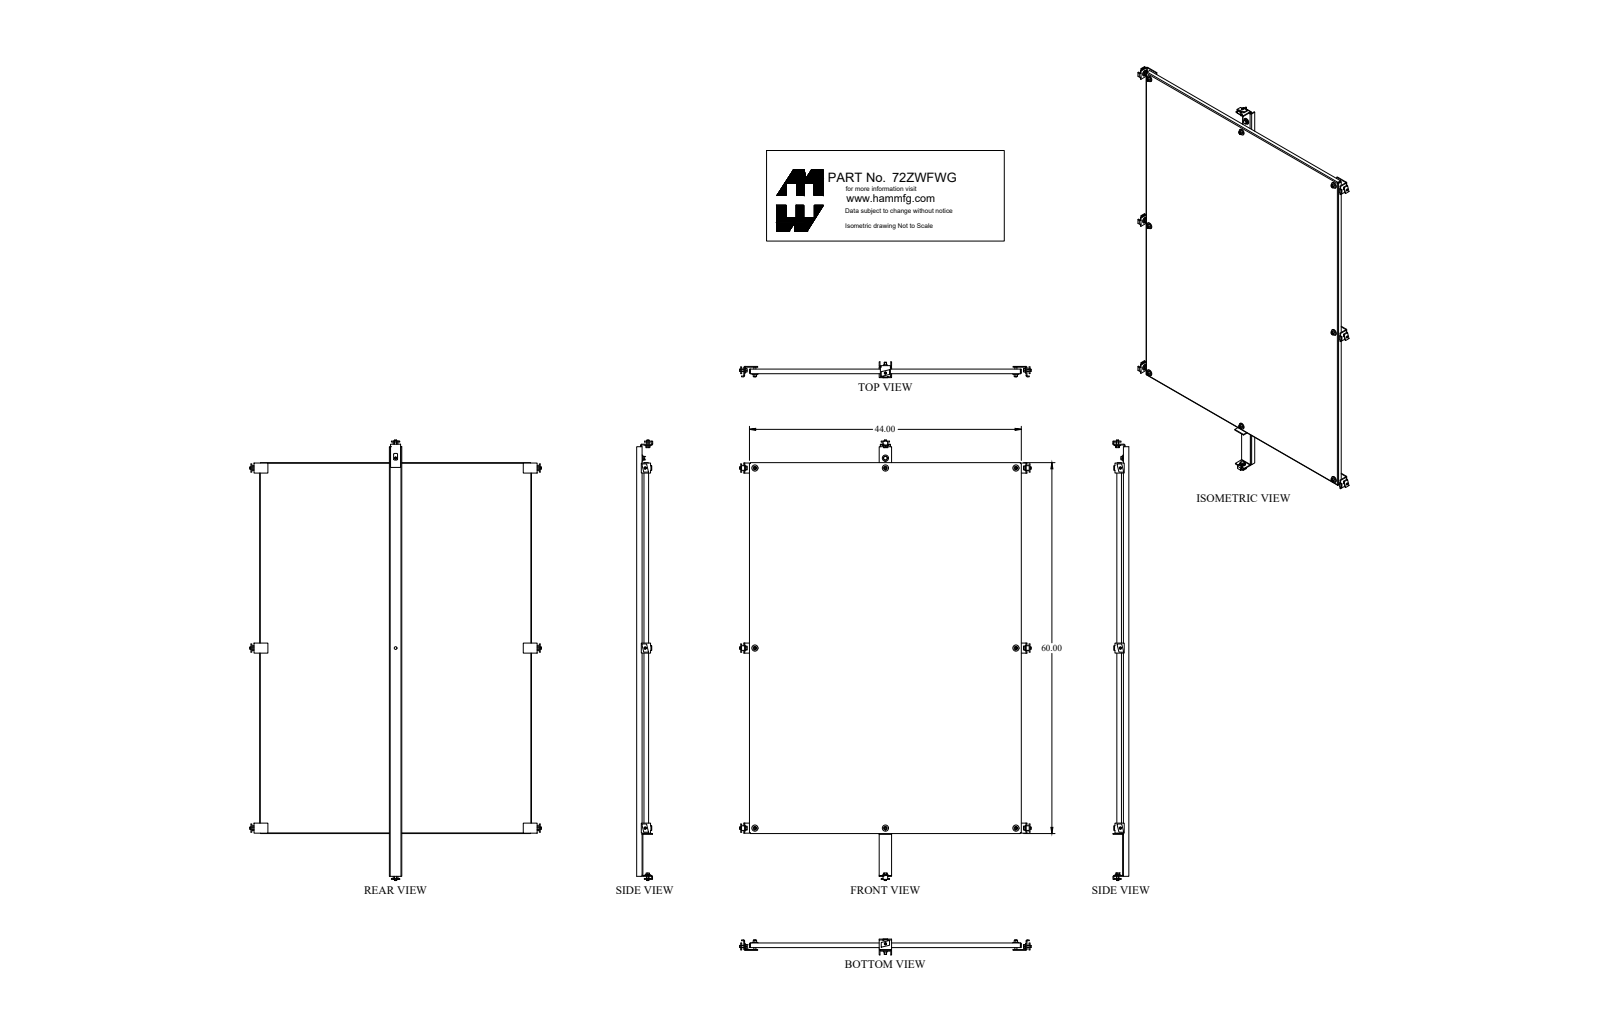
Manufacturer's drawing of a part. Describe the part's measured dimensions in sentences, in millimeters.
The part is named "72ZWFWG_Default". Its 3-D file was written by "SolidWorks 2018 (CONFIG_CONTROL_DESIGN)". It is 18 solids with 385 faces: 188 planar, 133 cylindrical and 64 other. Overall it measures 1801 by 1183.2 by 65.9 millimeters. Its volume is 4 942 000 cubic millimeters and its surface area 4 003 000 square millimeters. Round holes: 8 of diameter 14.3, 5 of diameter 11.1, 1 of diameter 11.1, 1 of diameter 11.5. Round bosses or shafts: 8 of diameter 16.5, 8 of diameter 8.4, 6 of diameter 9.5, 2 of diameter 9.5. Partial cylindrical surfaces (rounded edges, fillets, slot ends): 11 of radius 1.5, 11 of radius 4.7, 4 of radius 1.2, 4 of radius 3.6, 2 of radius 5.6. The main face-to-face distances are 2.4, 3.2, 29.4, 26.2, 23.8, 27, 533.4, 584.2, 1115.2, 531. The hole center spacings are 913.9, 536.6, 739.8, 1303.4, 1573.8, 1073.2, 1479.6, 739.9.
